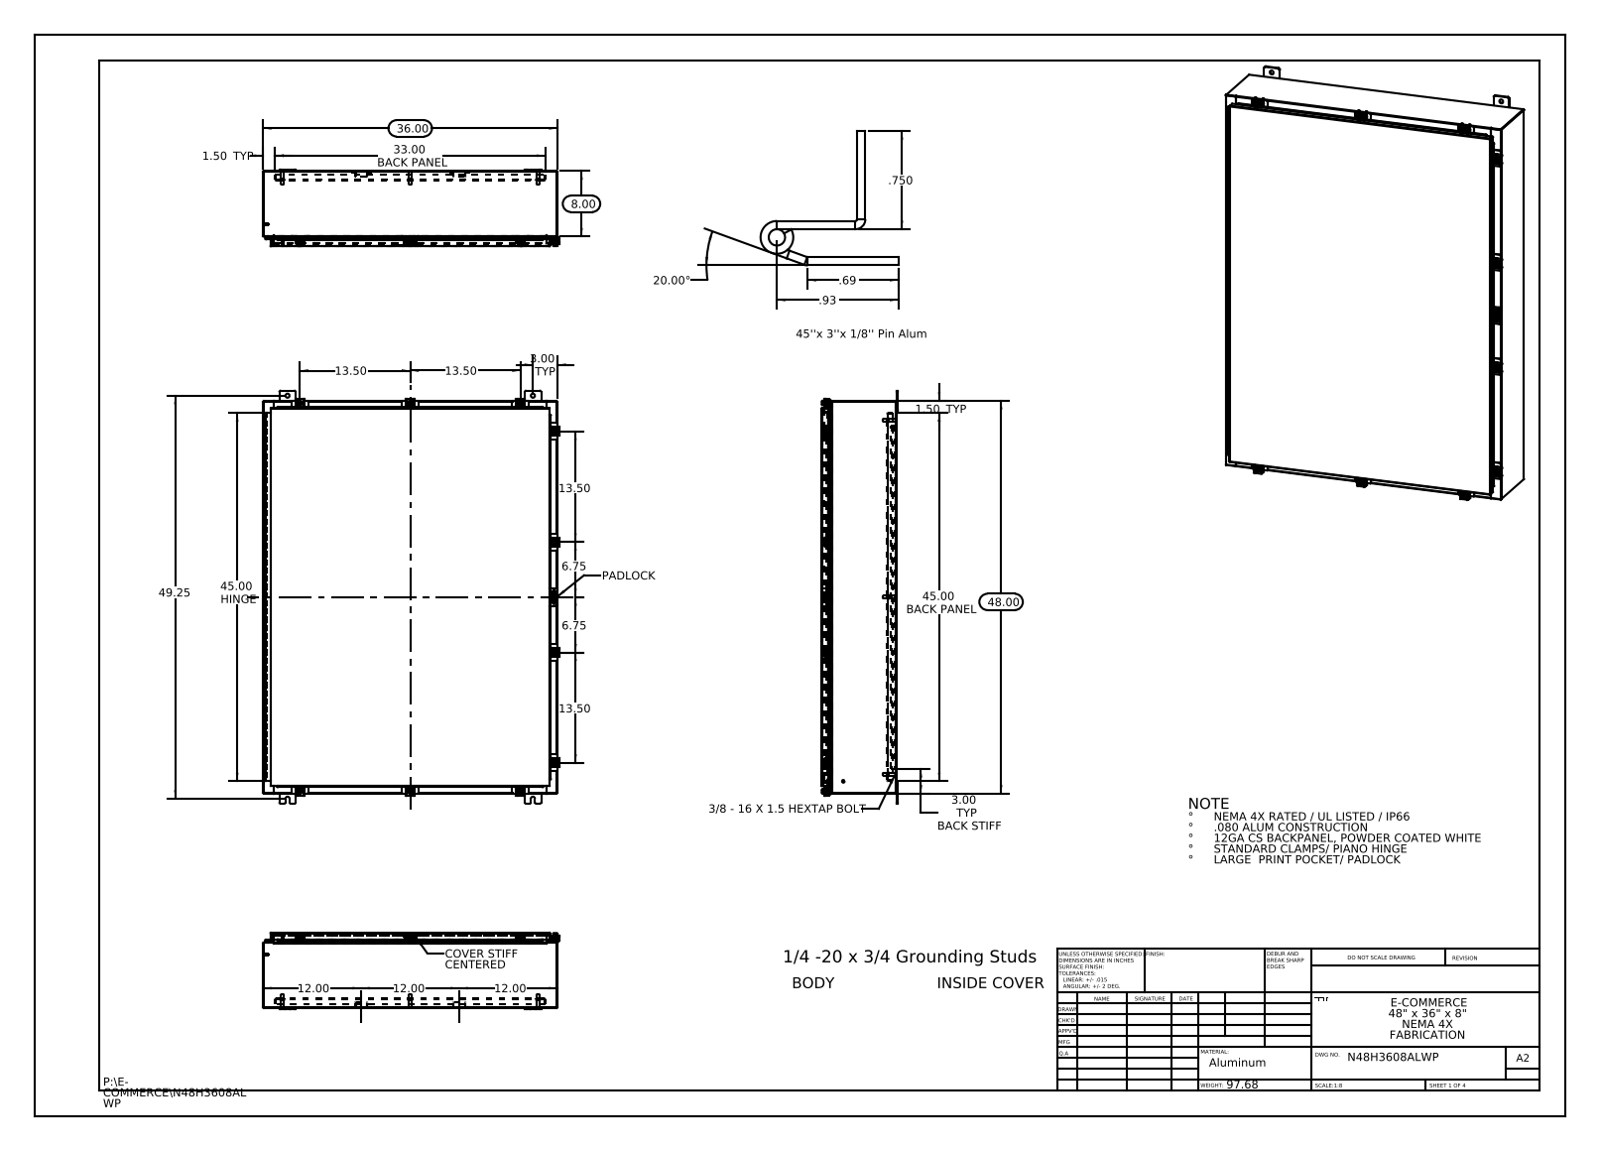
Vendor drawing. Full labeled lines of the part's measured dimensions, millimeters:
Part name (STEP PRODUCT): N48H3608ALWP Mounting Feet; N48H3608ALWP Body; N48H3608ALWP Mounting Studs; N48H3608ALWP (+8 more)
STEP written by: SolidWorks 2013 (CONFIG_CONTROL_DESIGN)
Units: millimetres
Bodies: 82 solids, 3115 faces (1586 planar, 1301 cylindrical, 228 other)
Overall size (bounding box): 1282.7 × 919.8 × 238.5
Volume: 9 847 000 mm³ · Surface area: 9 626 000 mm²
Round holes (diameter × count): ⌀12.7 ×12, ⌀5.4 ×10, ⌀6.6 ×10, ⌀6.4 ×6, ⌀3.2 ×2, ⌀3.2 ×1
Round bosses / shafts (diameter × count): ⌀6.4 ×11, ⌀12.7 ×10, ⌀10.1 ×10, ⌀15.9 ×8, ⌀9.5 ×8, ⌀8.4 ×8, ⌀4 ×6, ⌀3.6 ×6
Partial cylindrical surfaces — rounded edges, fillets, slot ends (radius × count): R1.5 ×46, R0.3 ×39, R2.2 ×33, R4.8 ×24, R3 ×20, R3.6 ×20, R1.3 ×15, R2 ×14
Main face-to-face distances: 1.9, 231.8, 229.9, 2.6, 233.7, 25.4, 206.4, 27.3, 204.5, 29.9
Hole centre spacings: 342.9, 347, 508, 511.1, 549.3, 605, 685.8, 965.3
